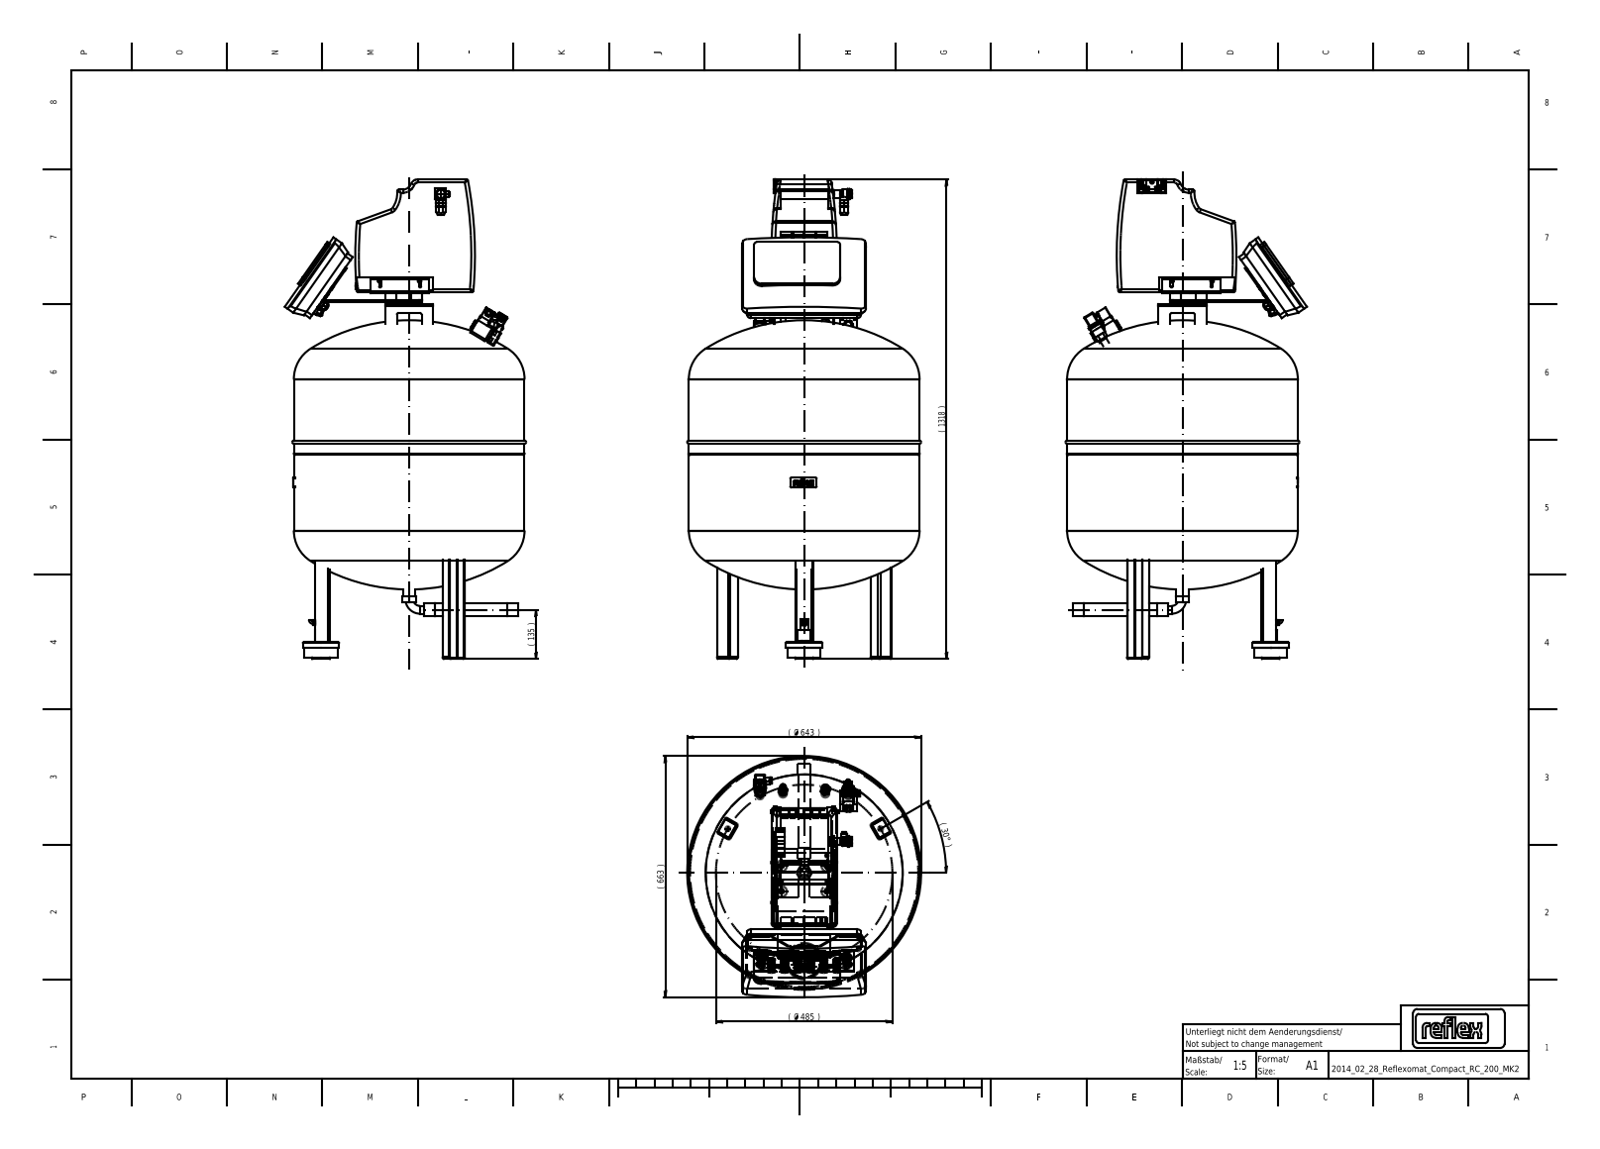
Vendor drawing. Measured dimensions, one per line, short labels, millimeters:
written by: Mechanical Desktop 2011 (CONFIG_CONTROL_DESIGN)
unit: mm
bodies: 42 solids, 2542 faces (1705 planar, 419 cylindrical, 418 other)
size: 1318 × 663.31 × 642.8
volume: 219 800 000 mm³; area: 4 586 000 mm²
holes: 8× ⌀8.2, 8× ⌀10.5, 7× ⌀17, 4× ⌀5.5, 4× ⌀9, 2× ⌀10, 2× ⌀13.4, 1× ⌀2, 1× ⌀6.5, 1× ⌀7, 1× ⌀14, 1× ⌀20
bosses: 8× ⌀19, 8× ⌀16, 8× ⌀8, 7× ⌀17.5, 4× ⌀30, 3× ⌀21.3, 3× ⌀19.8, 2× ⌀35
rounds: 31× R2.5, 23× R5, 14× R8, 11× R10, 10× R1, 6× R3, 4× R3.94, 4× R4.5
face distances: 416, 4, 2.5, 22, 2, 47.5, 655, 239, 26, 633
hole spacings: 125, 36, 22, 70, 72, 125.14, 126.92, 128.1
